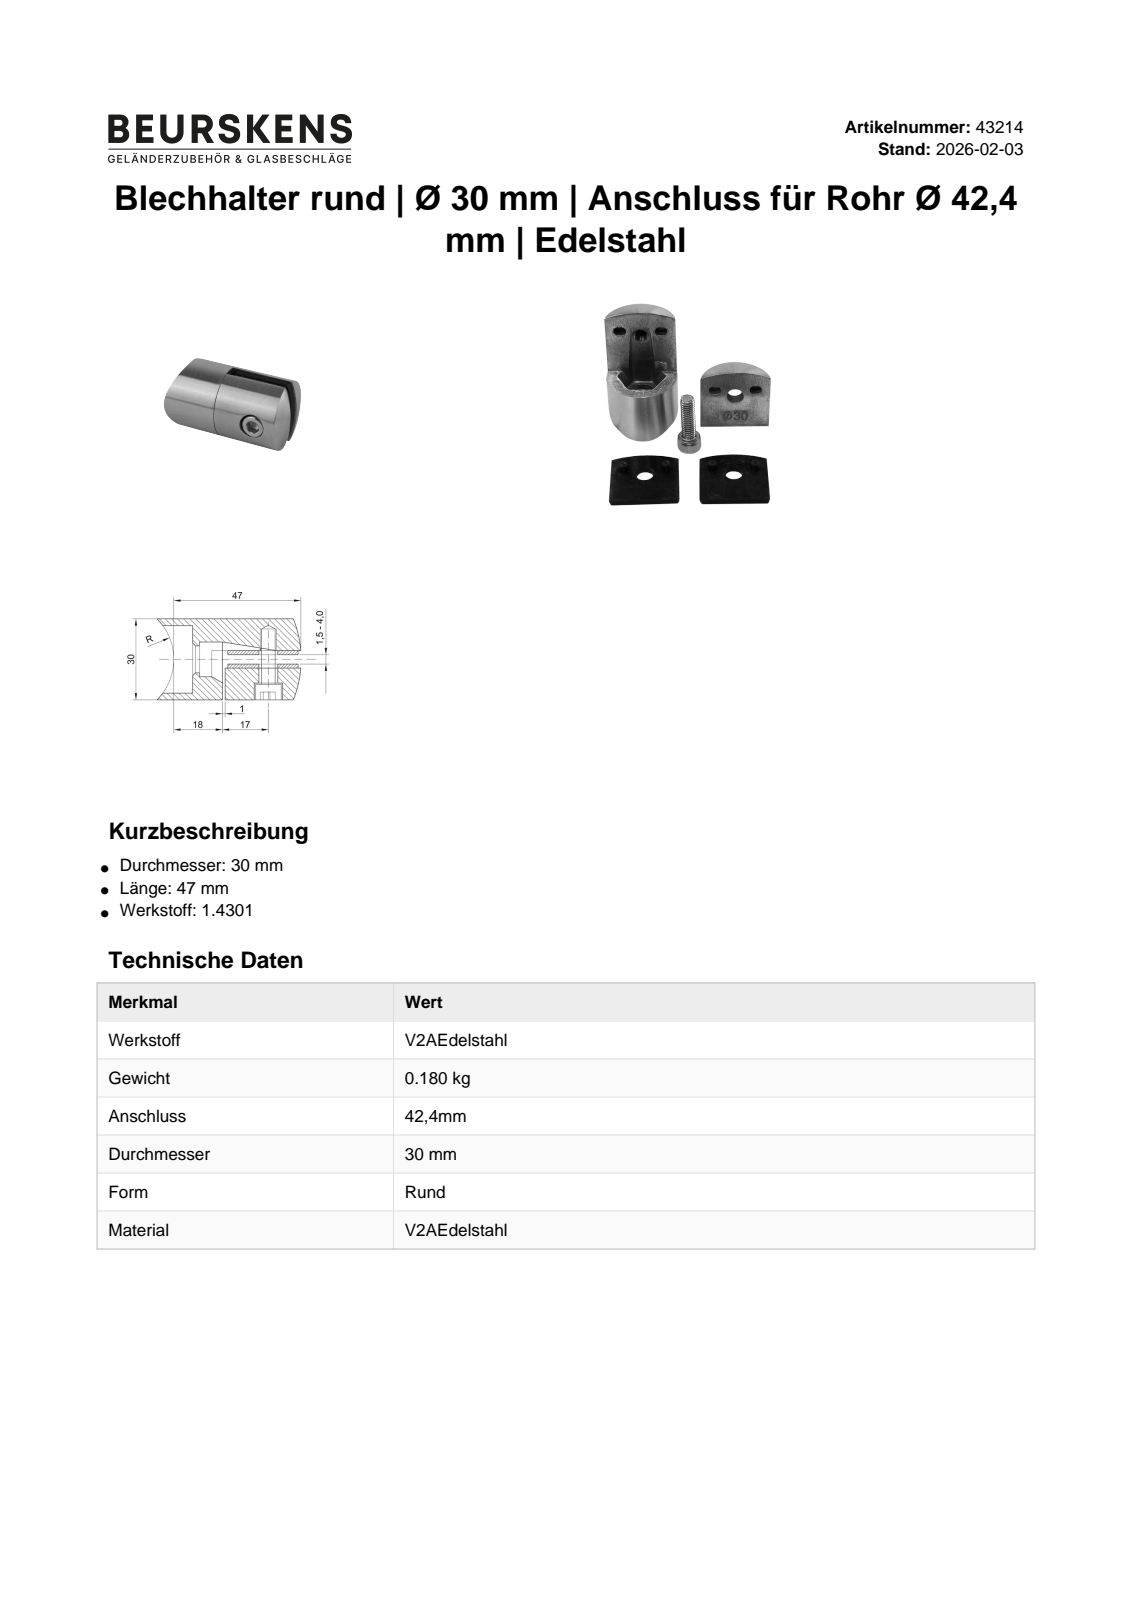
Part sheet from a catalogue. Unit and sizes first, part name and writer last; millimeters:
Units: millimetres
Overall size (bounding box): 49.69 × 30 × 30
Round holes (diameter × count): ⌀6 ×1, ⌀10 ×1, ⌀10.5 ×1, ⌀20 ×1
Round bosses / shafts (diameter × count): ⌀30 ×1, ⌀10 ×1
Partial cylindrical surfaces — rounded edges, fillets, slot ends (radius × count): R42.4 ×1, R81.95 ×1
Main face-to-face distances: 5, 1, 4, 6, 16, 7, 17.32, 9, 10, 11
Volume: 25 682 mm³ · Surface area: 9 810 mm²
Bodies: 3 solids, 50 faces (32 planar, 12 cylindrical, 6 other)
Part name (STEP PRODUCT): 43214; DIN 912 - M6 x 1 x 12 x 9,5
STEP written by: Autodesk Inventor 2022 (AUTOMOTIVE_DESIGN)
